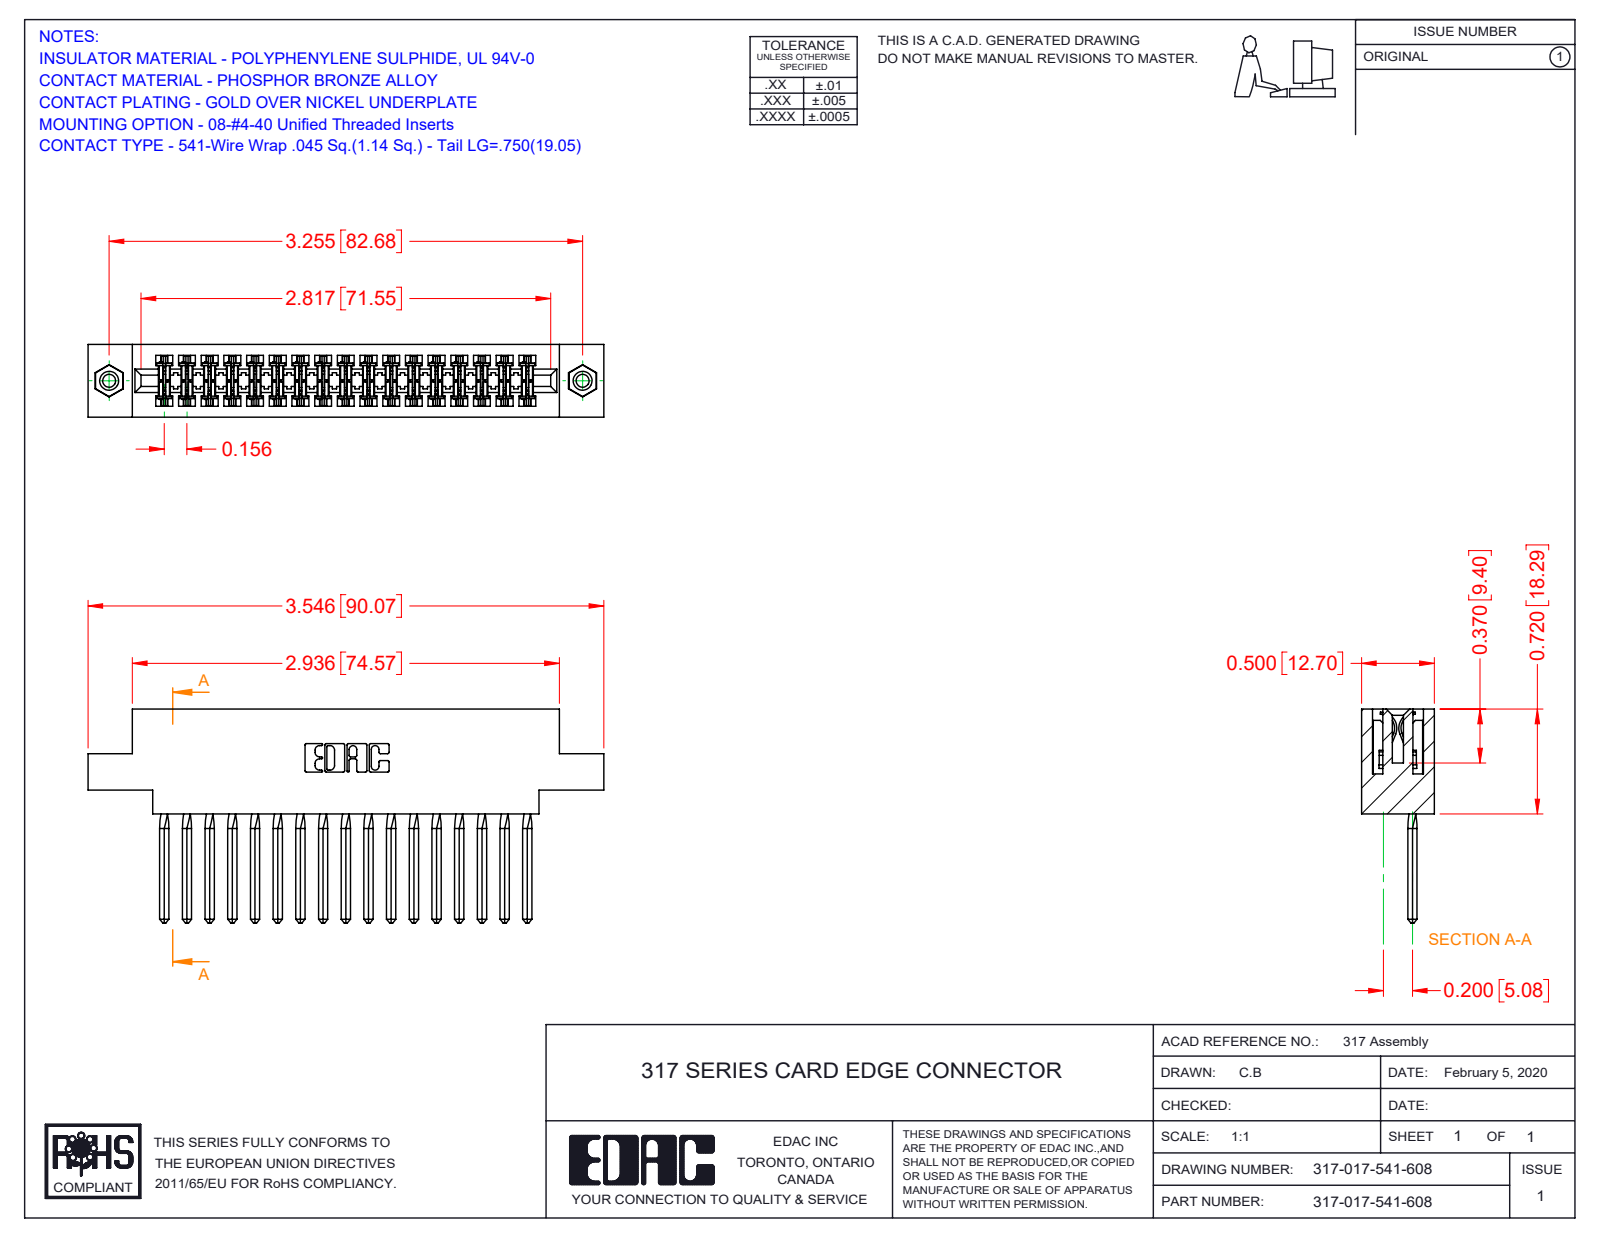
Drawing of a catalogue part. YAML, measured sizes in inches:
part_name: "317-290-002_541; 317-017-541-678; 317 Part_.156 Dia - TI; 345-250-001_345-250-003-102"
step_written_by: "SolidWorks 2016 (CONFIG_CONTROL_DESIGN)"
units: inches
bodies: {solids: 20, faces: 2746, planar: 2198, cylindrical: 464, other: 84}
overall_size: [3.546, 1.47, 0.5]
volume: 0.844
surface_area: 29.03
round_holes:
  - {diameter: 0.089, count: 2}
  - {diameter: 0.125, count: 2}
  - {diameter: 0.156, count: 2}
round_bosses_or_shafts:
  - {diameter: 0.155, count: 2}
partial_cylinders:
  - {radius: 0.015, count: 34}
  - {radius: 0.01, count: 22}
  - {radius: 0.007, count: 6}
  - {radius: 0.031, count: 6}
  - {radius: 0.026, count: 3}
  - {radius: 0.095, count: 2}
  - {radius: 0.1, count: 2}
  - {radius: 0.11, count: 2}
face_to_face_distances: [0.5, 0.075, 0.425, 0.11, 0.35, 0.22, 0.195, 0.772, 0.72, 0.136]
hole_center_spacings: [3.255]
